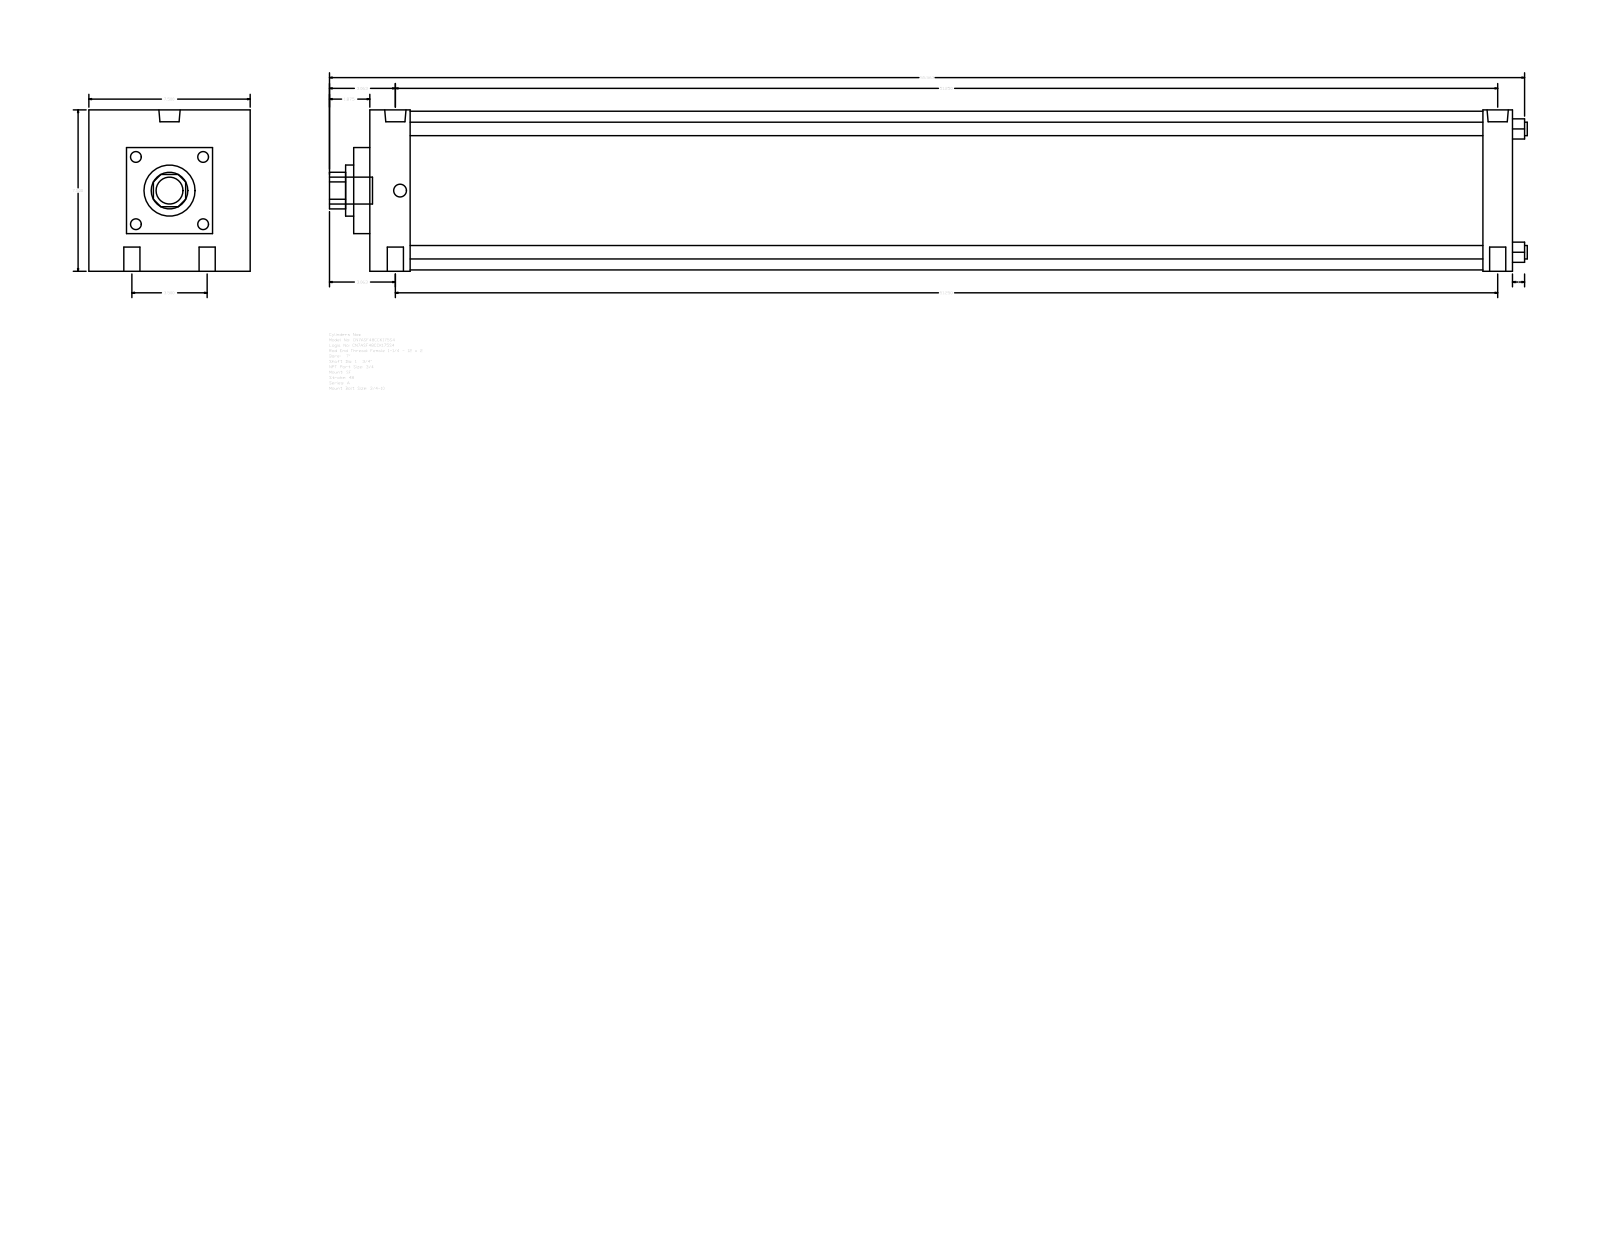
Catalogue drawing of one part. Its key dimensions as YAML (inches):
part_name: "A_SF__0700_1.75"
step_written_by: "GSSL Pune (CONFIG_CONTROL_DESIGN)"
units: inches
bodies: {solids: 0, faces: 93, planar: 67, cylindrical: 26, other: 0}
overall_size: [55.687, 7.5, 7.5]
round_holes:
  - {diameter: 0.75, count: 4}
  - {diameter: 0.594, count: 2}
  - {diameter: 0.989, count: 2}
  - {diameter: 1.75, count: 1}
  - {diameter: 2.375, count: 1}
round_bosses_or_shafts:
  - {diameter: 0.625, count: 4}
  - {diameter: 7.375, count: 1}
  - {diameter: 1.25, count: 1}
partial_cylinders:
  - {radius: 0.852, count: 1}
face_to_face_distances: [7.5, 53.125, 1.75, 1.375, 0.75, 1.875, 51.75, 49.875, 51.25, 5.75]
hole_center_spacings: [1.75, 51.28, 51.25, 3.5, 51.369, 50.812]
